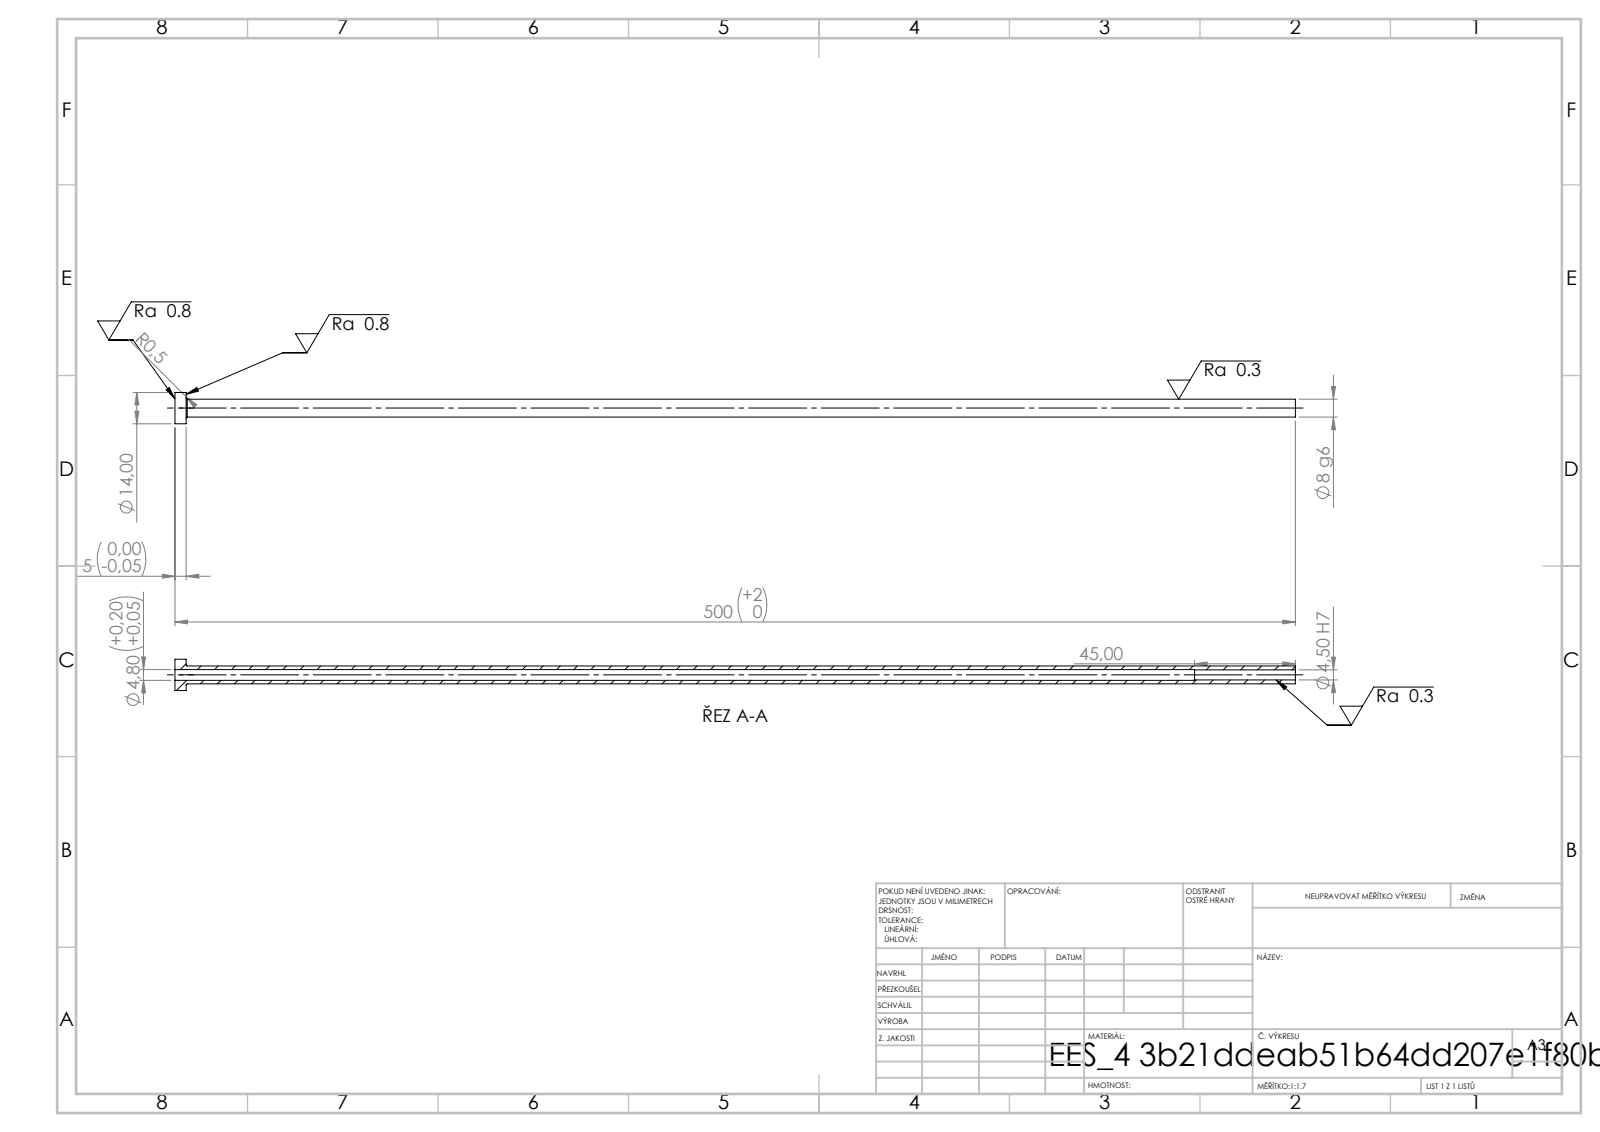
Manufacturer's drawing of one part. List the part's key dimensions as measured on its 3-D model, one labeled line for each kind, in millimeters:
STEP written by: SolidWorks 2019 (CONFIG_CONTROL_DESIGN)
Units: millimetres
Bodies: 1 solid, 14 faces (4 planar, 8 cylindrical, 2 other)
Overall size (bounding box): 500 × 14 × 14
Volume: 16 703 mm³ · Surface area: 20 429 mm²
Round holes (diameter × count): ⌀4.5 ×1, ⌀4.8 ×1
Round bosses / shafts (diameter × count): ⌀14 ×1, ⌀8 ×1
Main face-to-face distances: 5, 500, 495, 455, 450, 45
